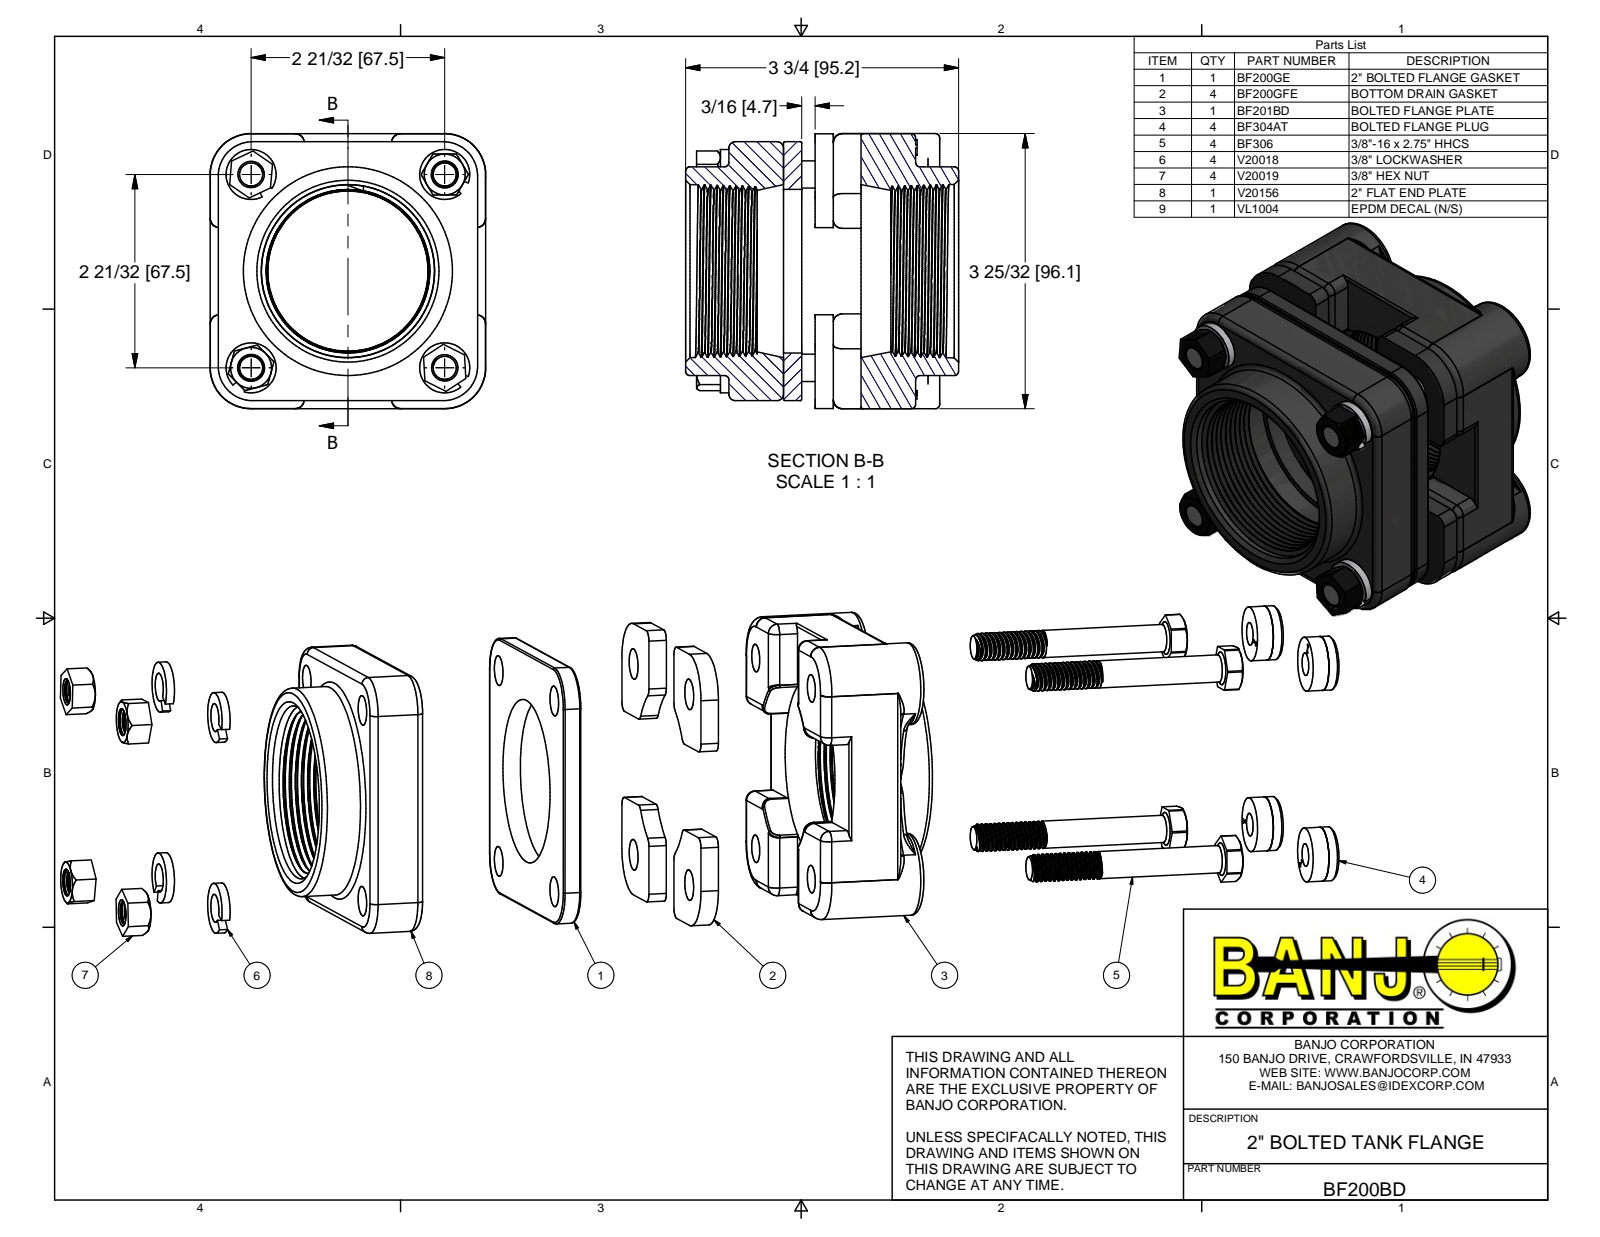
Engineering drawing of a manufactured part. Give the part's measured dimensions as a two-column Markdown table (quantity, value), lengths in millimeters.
| quantity | value |
| --- | --- |
| part name | BF200GE; V20156; V20019; V20018 (+6 more) |
| STEP written by | Autodesk Inventor 2016 (AUTOMOTIVE_DESIGN) |
| units | millimeters |
| bodies | 23 solids, 1395 faces (419 planar, 399 cylindrical, 577 other) |
| overall size | 96.11 × 96.11 × 95.21 |
| volume | 390 892 mm³ |
| surface area | 120 679 mm² |
| round holes (diameter × count) | 7.81 × 4, 9.65 × 4, 9.78 × 4, 10.31 × 4, 10.41 × 4, 10.72 × 4, 18.16 × 4, 19.05 × 4, 57.15 × 1 |
| round bosses / shafts (diameter × count) | 8.24 × 60, 28.57 × 4, 18.85 × 4, 17.46 × 4, 9.52 × 4, 72.9 × 1 |
| partial cylindrical surfaces (radius × count) | 3.17 × 40, 0.51 × 16, 1.52 × 12, 2.29 × 8, 4.12 × 8, 30.23 × 5, 0.76 × 4, 8.12 × 4 |
| main face-to-face distances | 6.35, 11.03, 17.38, 2.82, 93.24, 19.05, 4.68, 46.09, 25.4, 30.08 |
| hole center spacings | 47.76, 67.54, 95.52 |
